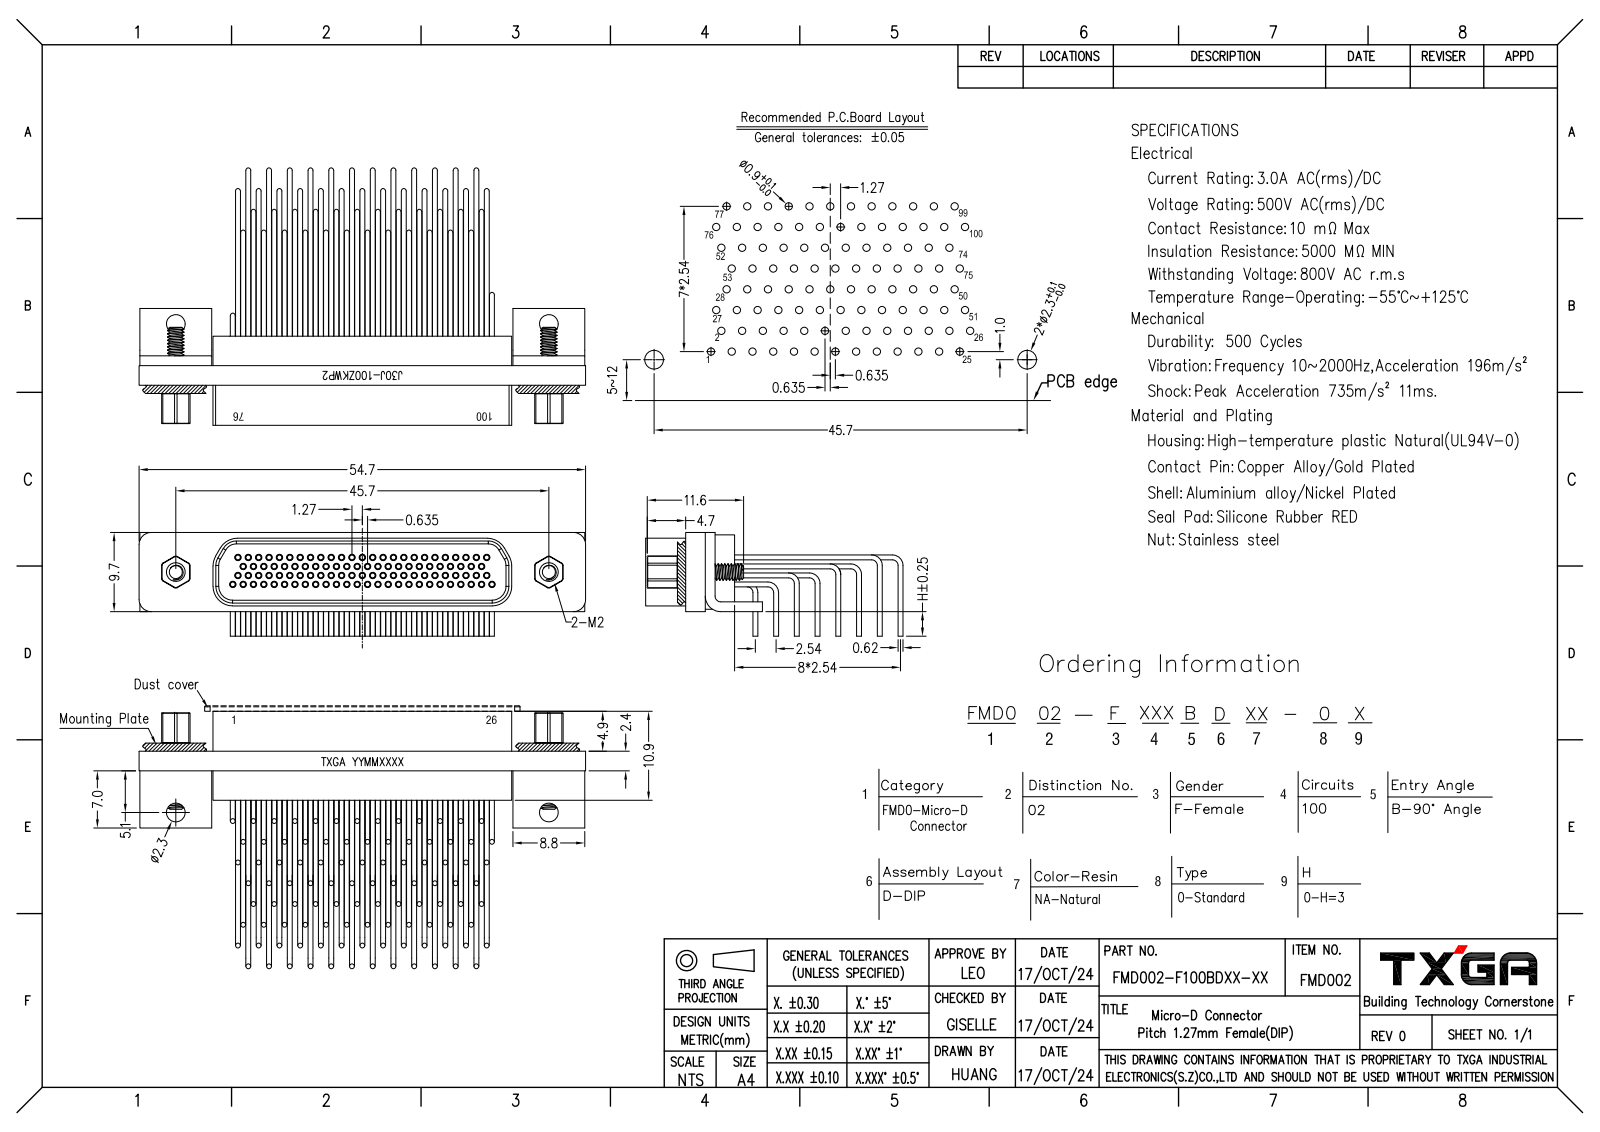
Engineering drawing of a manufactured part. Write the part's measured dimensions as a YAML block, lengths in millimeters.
part_name: "FMD002-F100BDNA-00"
step_written_by: "SolidWorks 2021 (CONFIG_CONTROL_DESIGN)"
units: millimeters
bodies: {solids: 1, faces: 2540, planar: 847, cylindrical: 962, other: 731}
overall_size: [54.7, 31.52, 12.7]
volume: 3739
surface_area: 8219
round_holes:
  - {diameter: 0.6, count: 100}
  - {diameter: 1.6, count: 2}
  - {diameter: 1.8, count: 2}
  - {diameter: 2.3, count: 2}
  - {diameter: 3.2, count: 2}
round_bosses_or_shafts:
  - {diameter: 0.8, count: 100}
  - {diameter: 0.6, count: 100}
  - {diameter: 2, count: 2}
partial_cylinders:
  - {radius: 0.3, count: 12}
  - {radius: 1.5, count: 8}
  - {radius: 2.4, count: 6}
  - {radius: 2, count: 4}
  - {radius: 1.7, count: 2}
  - {radius: 0.7, count: 1}
  - {radius: 1.9, count: 1}
face_to_face_distances: [0.7, 8.3, 6, 7.6, 1.4, 9, 9.4, 0.4, 1.1, 8]
hole_center_spacings: [1.27, 3.36, 2.54, 2.2, 4.58, 5.08, 5.82, 3.81]
